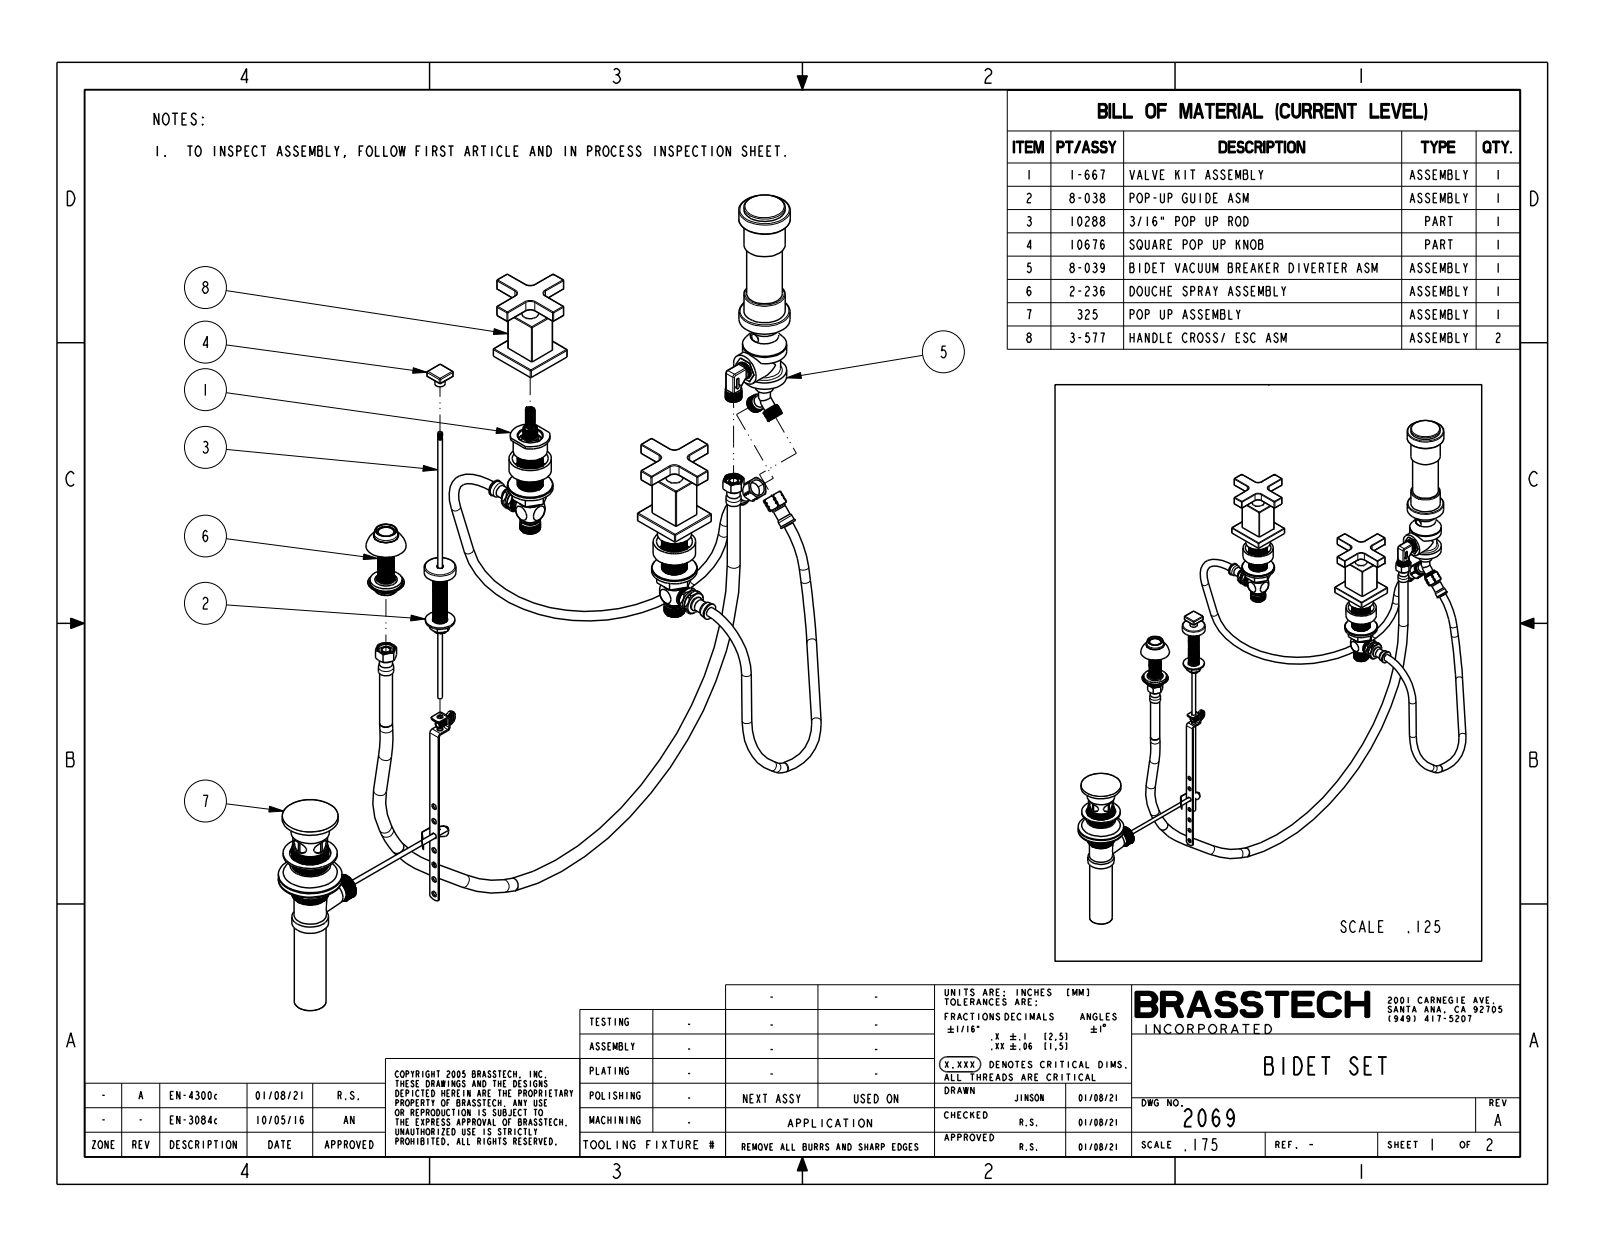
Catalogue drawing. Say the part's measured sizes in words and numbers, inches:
The part is named "2069". Its 3-D file was written by "CREO PARAMETRIC BY PTC INC, 2018400 (CONFIG_CONTROL_DESIGN)". It is 5 solids with 364 faces: 98 planar, 158 cylindrical and 108 other. Overall it measures 22.8 by 11.14 by 5.445 inches. Its volume is 24.06 cubic inches and its surface area 114.7 square inches. Round holes: 1 of diameter 0.625, 1 of diameter 0.792, 1 of diameter 0.94. Round bosses or shafts: 2 of diameter 0.65, 2 of diameter 0.523, 1 of diameter 2.02, 1 of diameter 2, 1 of diameter 1.62, 1 of diameter 1.4, 1 of diameter 1.24, 1 of diameter 0.925. Partial cylindrical surfaces (rounded edges, fillets, slot ends): 68 of radius 0.03, 12 of radius 0.04, 8 of radius 0.25, 1 of radius 0.357. The main face-to-face distances are 8, 3.046, 2.596, 0.45, 0.35, 2.246, 2.696, 1.16, 1.34, 0.6.
